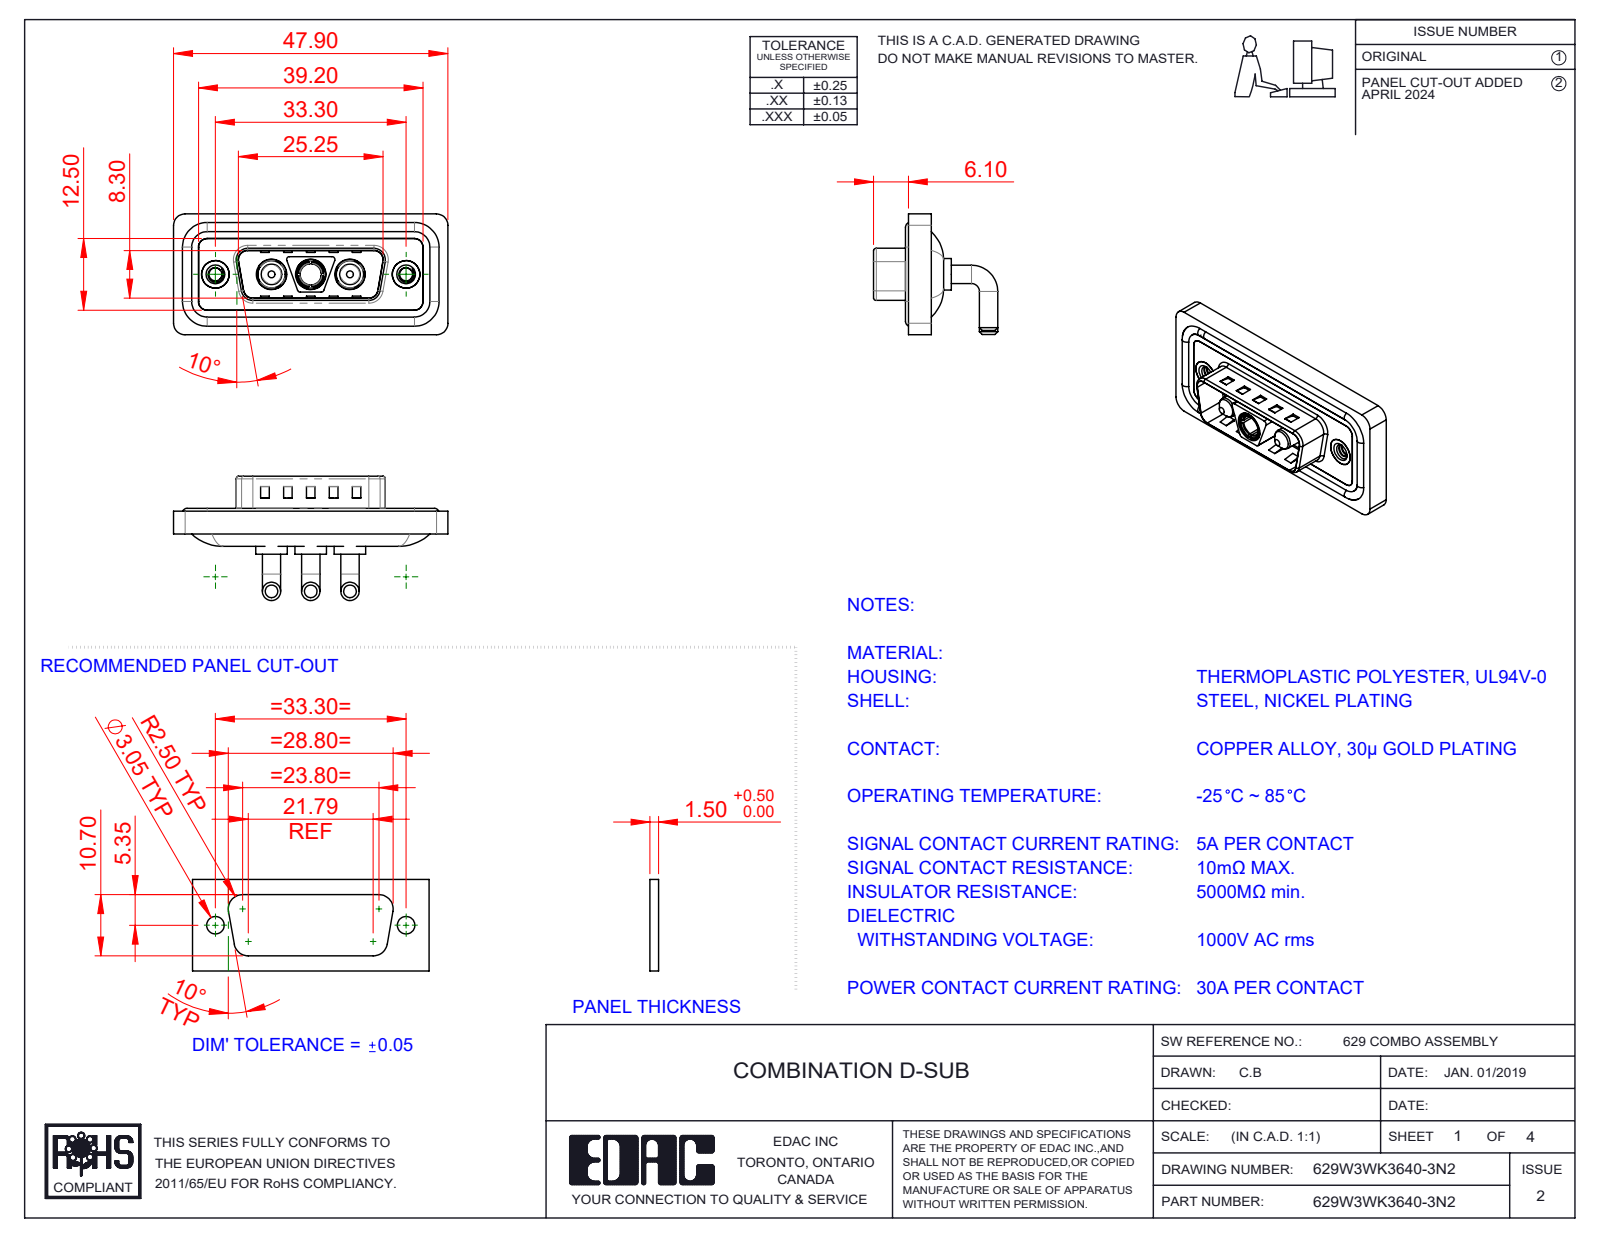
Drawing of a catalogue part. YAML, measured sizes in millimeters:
part_name: "629W3WK3640-3N2; 629Combo Waterproof Housing_15 Contacts; Power Pin_30A RA; 629Combo Threaded Rivet_2 (+4 more)"
step_written_by: "SolidWorks 2023 (CONFIG_CONTROL_DESIGN)"
units: millimeters
bodies: {solids: 13, faces: 621, planar: 231, cylindrical: 256, other: 134}
overall_size: [47.9, 21.7, 21.1]
volume: 5981
surface_area: 9472
round_holes:
  - {diameter: 4.85, count: 3}
  - {diameter: 5.3, count: 3}
  - {diameter: 2.26, count: 2}
  - {diameter: 4, count: 2}
  - {diameter: 4.8, count: 2}
  - {diameter: 5, count: 2}
  - {diameter: 3.7, count: 1}
round_bosses_or_shafts:
  - {diameter: 3.2, count: 6}
  - {diameter: 1.6, count: 4}
  - {diameter: 5.5, count: 3}
  - {diameter: 5.2, count: 3}
  - {diameter: 4.75, count: 3}
  - {diameter: 3.75, count: 3}
  - {diameter: 4.9, count: 2}
  - {diameter: 3.6, count: 2}
partial_cylinders:
  - {radius: 2, count: 20}
  - {radius: 1.5, count: 18}
  - {radius: 0.5, count: 12}
  - {radius: 1.6, count: 8}
  - {radius: 0.25, count: 4}
  - {radius: 0.6, count: 4}
  - {radius: 0.65, count: 4}
  - {radius: 0.9, count: 4}
face_to_face_distances: [0.4, 2.9, 0.8, 1.1, 2.1, 1.6, 3.1, 2.5, 4.5, 3.7]
hole_center_spacings: [6.85, 9.8, 16.65, 23.5, 13.7, 33.3]
